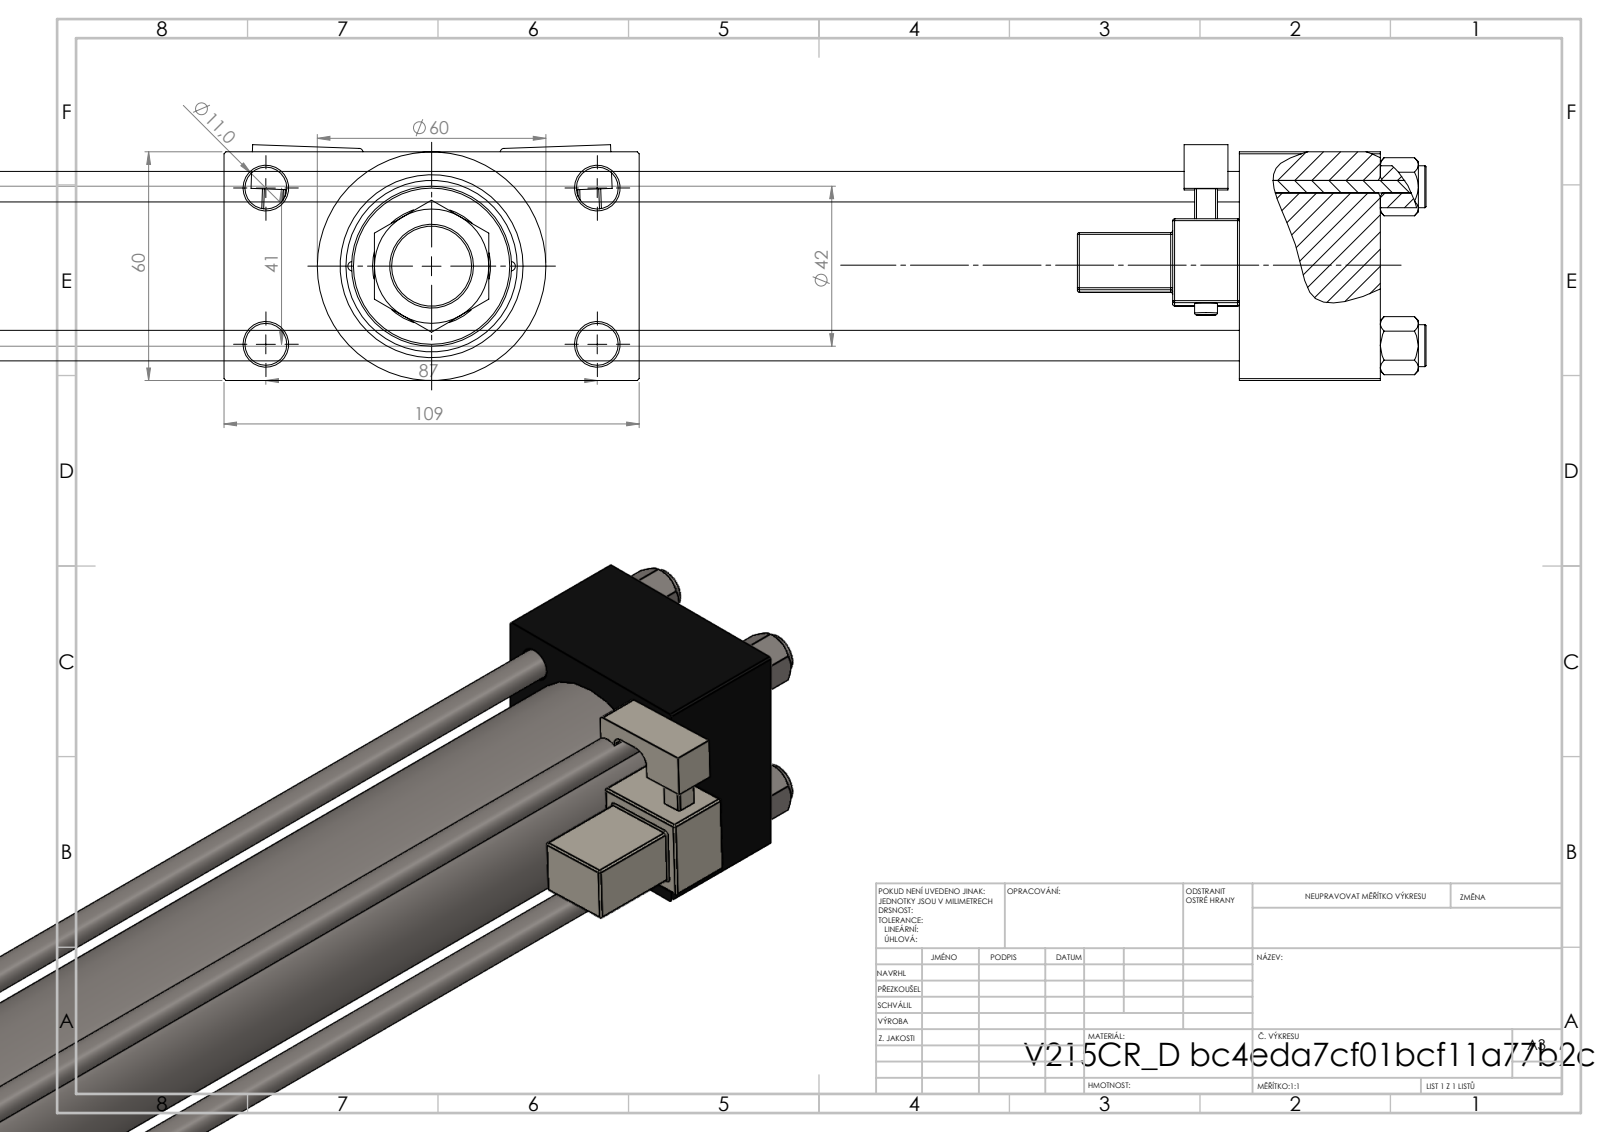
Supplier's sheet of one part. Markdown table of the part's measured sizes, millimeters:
| quantity | value |
| --- | --- |
| part name | V215CR_D_Body; MFA; NUT_M5_D; V215CR_MSU (+3 more) |
| STEP written by | SolidWorks 2019 (CONFIG_CONTROL_DESIGN) |
| units | millimeters |
| bodies | 14 solids, 1320 faces (576 planar, 156 cylindrical, 588 other) |
| overall size | 560 × 109 × 61.9 |
| volume | 997 422 mm³ |
| surface area | 298 114 mm² |
| round holes (diameter × count) | 8 × 4, 11 × 4, 2.5 × 2, 7 × 2, 16.66 × 2, 24 × 2, 18.5 × 1, 28 × 1, 31 × 1, 40 × 1, 45 × 1 |
| round bosses / shafts (diameter × count) | 11 × 4, 6 × 2, 60 × 1, 46 × 1, 42 × 1, 22 × 1, 14 × 1 |
| partial cylindrical surfaces (radius × count) | 0.5 × 48, 1 × 2, 2.5 × 2, 4 × 2, 13.5 × 1 |
| main face-to-face distances | 60, 388, 24.5, 84.5, 37, 425, 468, 431, 43, 109 |
| hole center spacings | 20.85, 22.65, 29.49, 30.62, 41.7, 46.53, 47.15, 48.09 |
